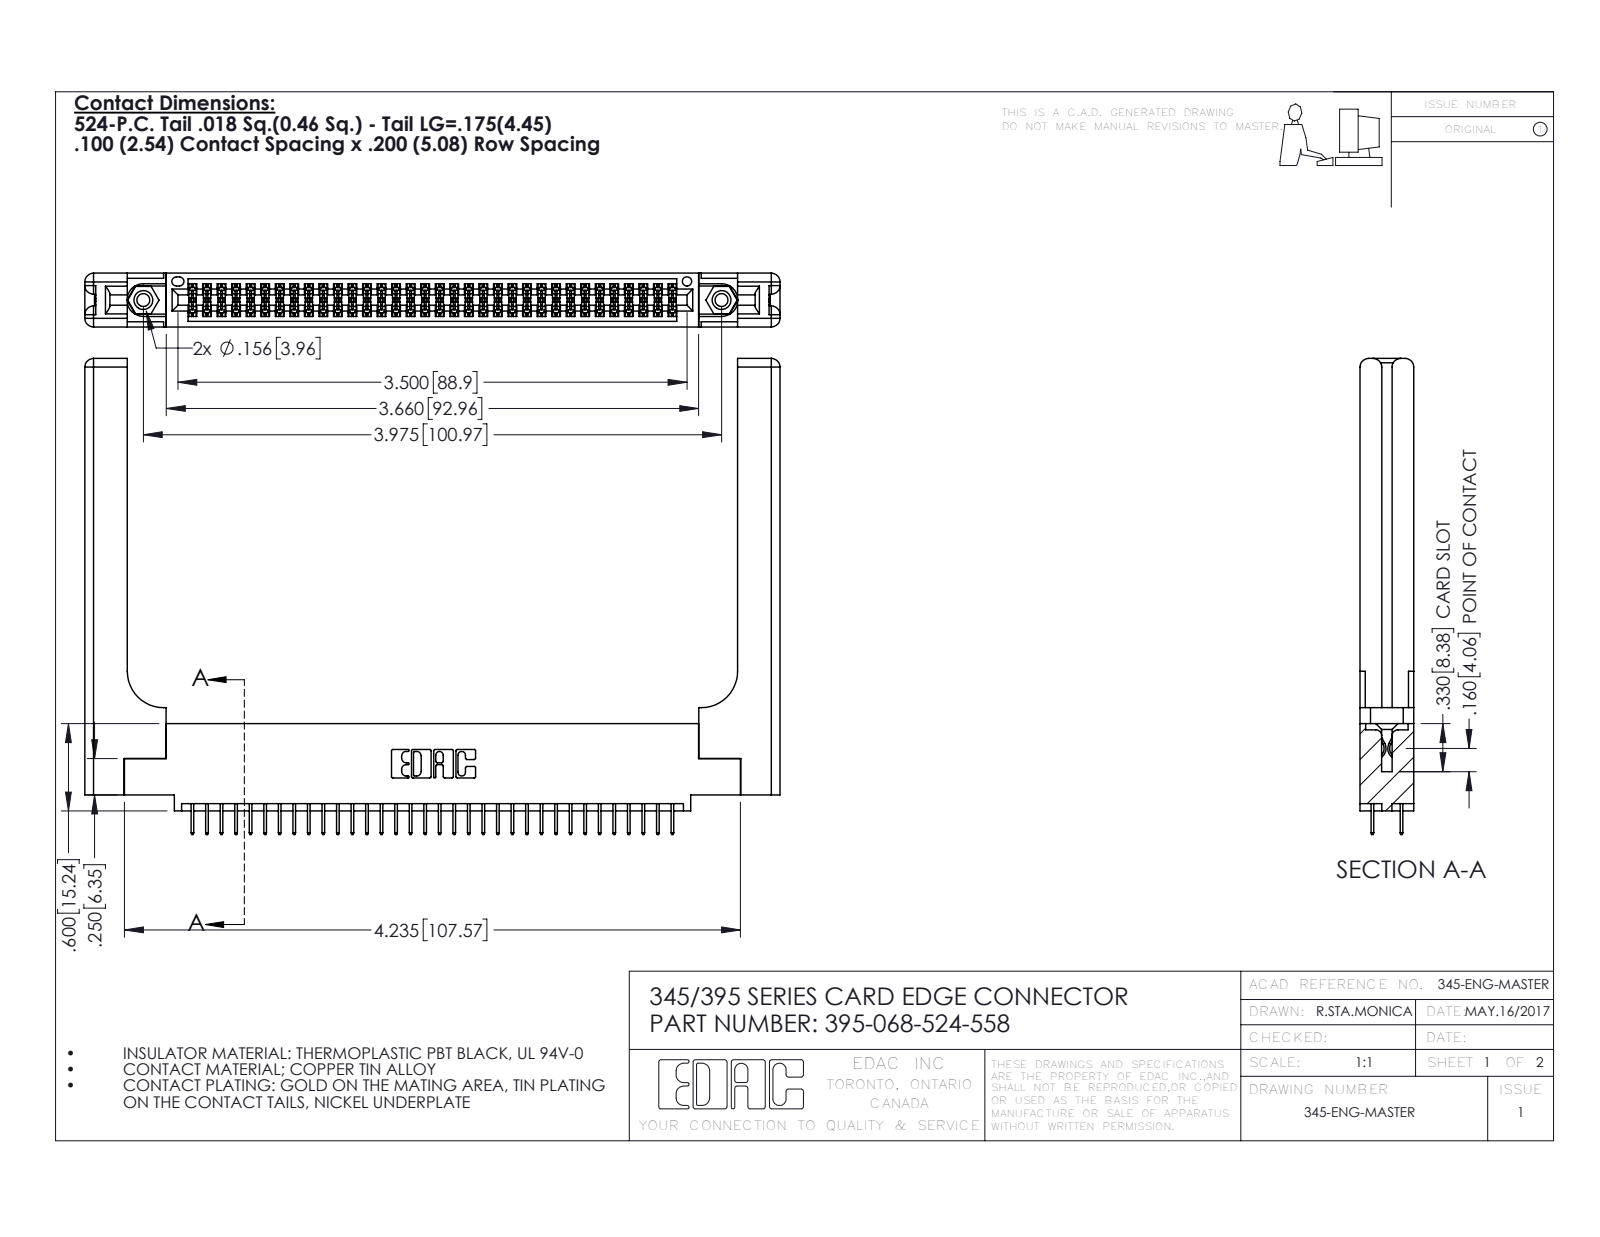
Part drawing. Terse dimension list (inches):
name: 345-250-001_345-250-001-102; 395-068-524-558; 345-220-058_345-220-058; 345 Part_0.110 Offset - 0.156 Dia-TH (+1 more)
written by: SolidWorks 2016 (CONFIG_CONTROL_DESIGN)
unit: in
bodies: 73 solids, 4058 faces (2884 planar, 1114 cylindrical, 60 other)
size: 4.779 × 3.272 × 0.37
volume: 1.221 in³; area: 33.77 in²
holes: 2× ⌀0.089, 2× ⌀0.125, 2× ⌀0.156, 1× ⌀0.064
bosses: 2× ⌀0.155
rounds: 102× R0.006, 22× R0.01, 16× R0.06, 6× R0.007, 6× R0.031, 3× R0.026, 2× R0.014, 2× R0.019
face distances: 0.37, 0.072, 0.298, 0.2, 0.098, 0.272, 0.025, 0.225, 0.148, 0.15
hole spacings: 0.27, 3.74, 3.975
